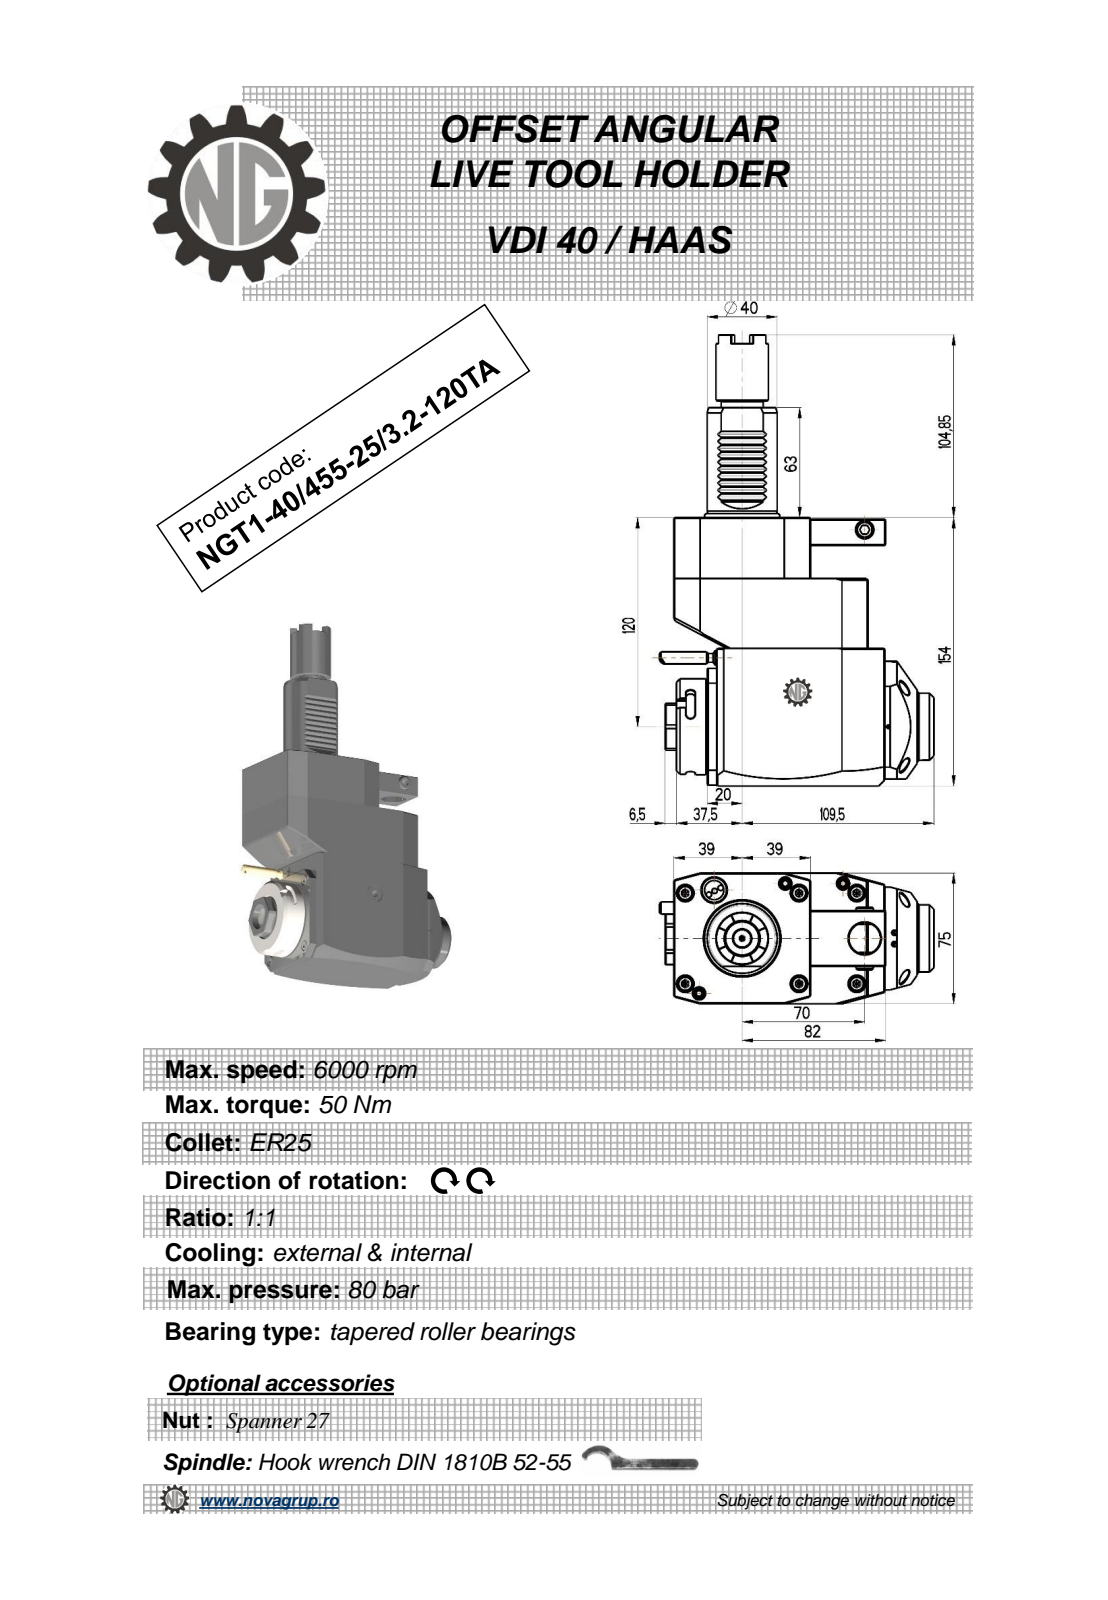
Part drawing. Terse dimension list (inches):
name: NGT1_40_455_25_3_2_120TA
written by: PRO/ENGINEER BY PARAMETRIC TECHNOLOGY CORPORATION, 2010280 (CONFIG_CONTROL_DESIGN)
unit: in
bodies: 1 solid, 378 faces (216 planar, 78 cylindrical, 84 other)
size: 10.191 × 6.174 × 2.953
volume: 79.94 in³; area: 147.5 in²
holes: 2× ⌀0.709, 1× ⌀0.098, 1× ⌀0.118, 1× ⌀0.374
bosses: 2× ⌀0.353, 1× ⌀2.165, 1× ⌀1.89, 1× ⌀1.575, 1× ⌀1.516, 1× ⌀1.181, 1× ⌀0.787, 1× ⌀0.394
rounds: 10× R0.012, 6× R0.098, 2× R7.087, 1× R0.02, 1× R0.167, 1× R0.591, 1× R0.965, 1× R1.476
face distances: 2.953, 6.063, 0.748, 4.685, 2.323, 4.37, 3.622, 1.378, 0.689, 2.106
hole spacings: 1.701, 2.956, 4.429
